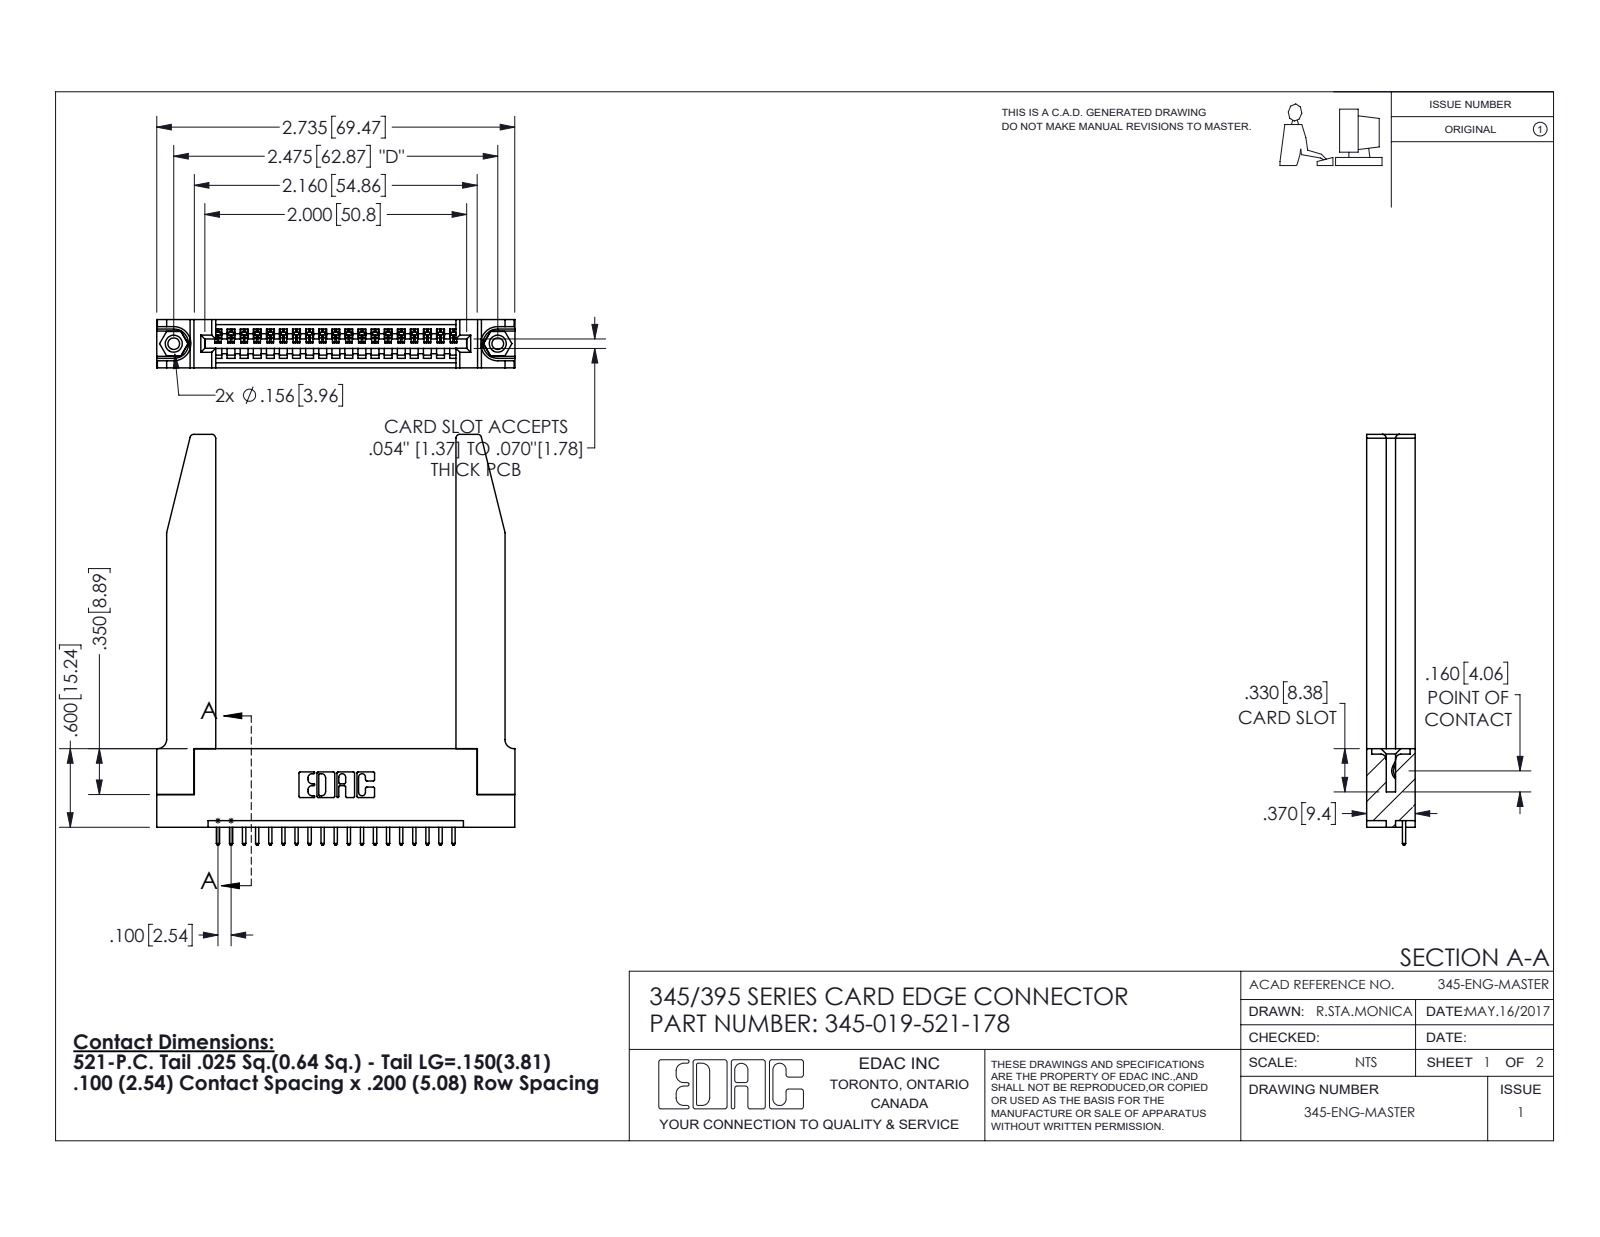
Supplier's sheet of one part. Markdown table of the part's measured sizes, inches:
| quantity | value |
| --- | --- |
| part name | 345-292-001_345-293-121; 345-019-521-178; 345 Part_Flush Mounting Lugs - 0.156 Dia-TH; 345-250-001_345-250-001-102 (+1 more) |
| STEP written by | SolidWorks 2016 (CONFIG_CONTROL_DESIGN) |
| units | inches |
| bodies | 24 solids, 1462 faces (982 planar, 428 cylindrical, 52 other) |
| overall size | 3.137 × 2.736 × 0.37 |
| volume | 0.862 in³ |
| surface area | 22.9 in² |
| round holes (diameter × count) | 0.089 × 2, 0.125 × 2, 0.156 × 2, 0.064 × 1 |
| round bosses / shafts (diameter × count) | 0.155 × 2 |
| partial cylindrical surfaces (radius × count) | 0.006 × 38, 0.01 × 38, 0.01 × 22, 0.03 × 8, 0.007 × 6, 0.031 × 6, 0.026 × 3, 0.031 × 2 |
| main face-to-face distances | 0.37, 0.072, 0.298, 0.2, 0.148, 0.15, 0.098, 0.272, 0.025, 0.077 |
| hole center spacings | 0.27, 2.241, 2.475 |
